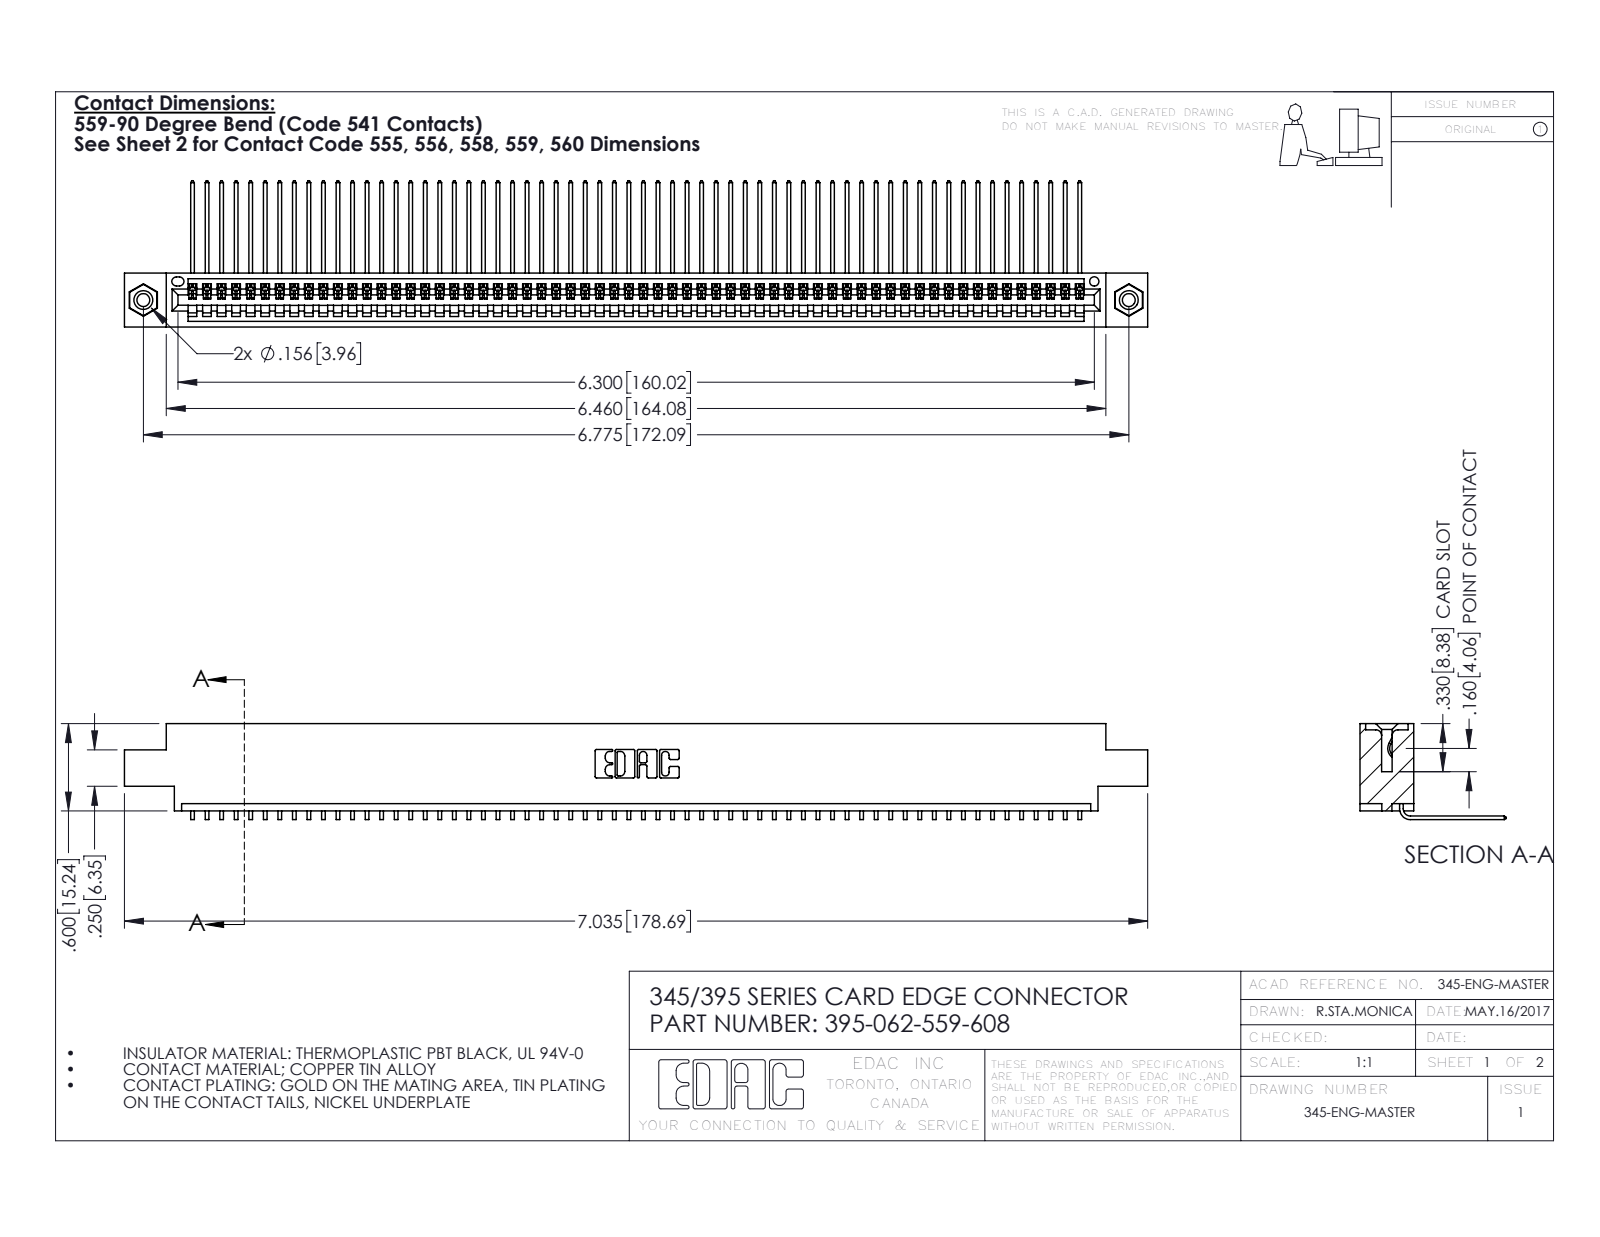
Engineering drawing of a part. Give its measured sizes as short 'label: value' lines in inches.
name: 345 Part_0.170 Offset - 0.156 Dia-TI; 345-292-001_558 559 Tail - 1; 395-062-559-608; 345-250-001_345-250-003-102
written by: SolidWorks 2016 (CONFIG_CONTROL_DESIGN)
unit: in
bodies: 65 solids, 3910 faces (2720 planar, 1174 cylindrical, 16 other)
size: 7.035 × 1.005 × 0.659
volume: 1.051 in³; area: 38 in²
holes: 2× ⌀0.089, 2× ⌀0.125, 2× ⌀0.156, 1× ⌀0.064
bosses: 2× ⌀0.155
rounds: 124× R0.006, 22× R0.01, 6× R0.007, 6× R0.031, 3× R0.026, 2× R0.031, 2× R0.04, 1× R0.014
face distances: 0.072, 0.298, 0.37, 0.2, 0.098, 0.272, 0.025, 0.225, 0.175, 0.149
hole spacings: 0.27, 6.539, 6.775
